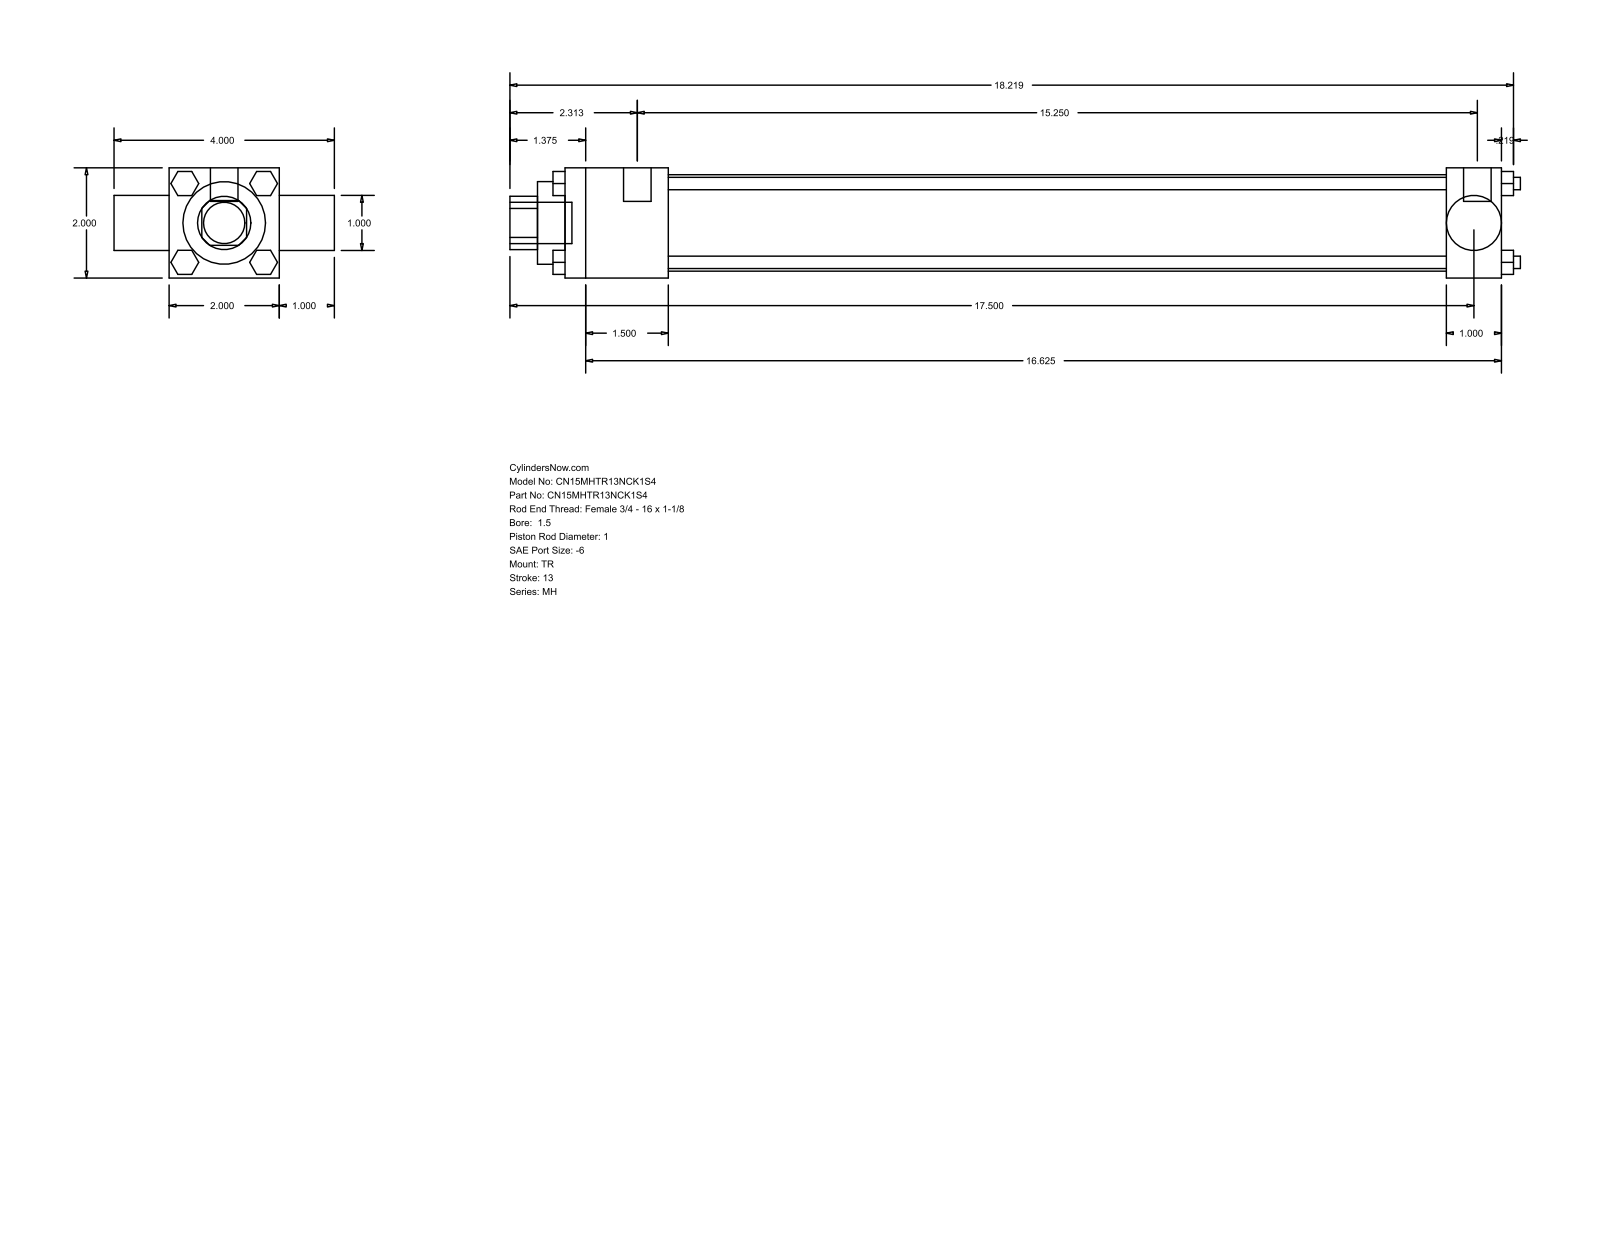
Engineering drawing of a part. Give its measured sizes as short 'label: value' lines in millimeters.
name: MH_TR__0150_1
written by: GSSL Pune (CONFIG_CONTROL_DESIGN)
unit: mm
bodies: 0 solids, 120 faces (92 planar, 28 cylindrical, 0 other)
size: 465.93 × 101.6 × 50.8
holes: 1× ⌀25.35, 1× ⌀25.4, 1× ⌀38.1, 1× ⌀44.45
bosses: 4× ⌀5.71, 3× ⌀5.56, 2× ⌀12.7, 1× ⌀19.05
rounds: 1× R12.29
face distances: 50.8, 25.4, 431.8, 76.2, 47.63, 384.17, 406.4, 358.77, 437.36, 12.7
